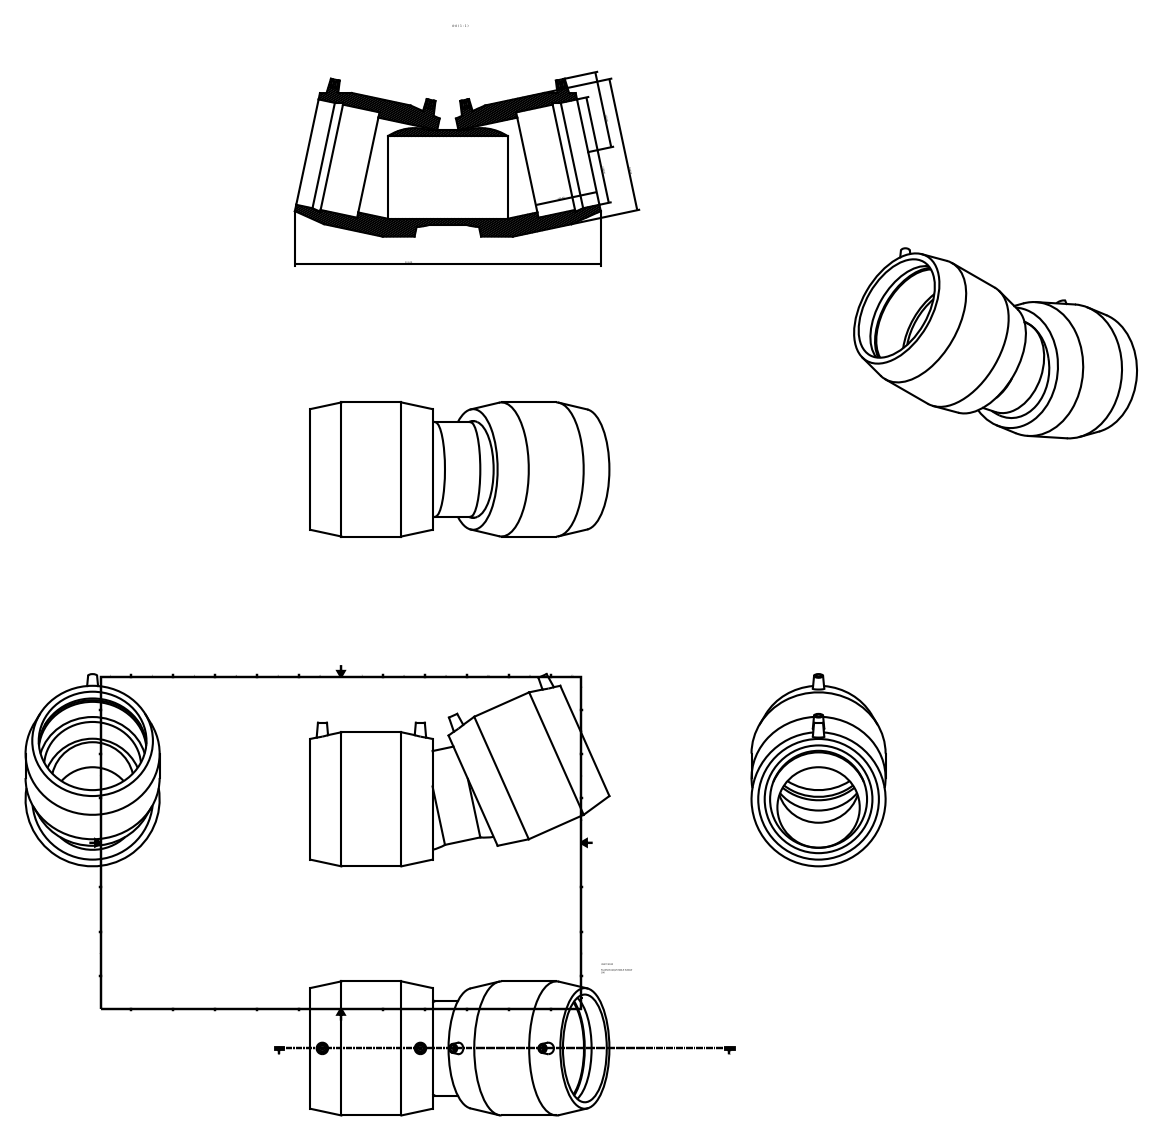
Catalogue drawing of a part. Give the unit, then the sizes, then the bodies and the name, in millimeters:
Units: millimetres
Overall size (bounding box): 499.83 × 321.2 × 224
Round holes (diameter × count): ⌀10 ×4, ⌀180 ×3, ⌀162 ×2, ⌀137.59 ×1
Round bosses / shafts (diameter × count): ⌀4 ×4, ⌀224 ×2, ⌀157.67 ×1
Main face-to-face distances: 204.4, 204.5, 104, 100.4, 100.45, 104.05, 41.6, 62.4, 162.8, 162.88
Hole centre spacings: 163.52
Volume: 6 773 000 mm³ · Surface area: 696 189 mm²
Bodies: 1 solid, 50 faces (20 planar, 18 cylindrical, 12 other)
Part name (STEP PRODUCT): 4947C4180
STEP written by: Autodesk Inventor 2015 (AUTOMOTIVE_DESIGN)
